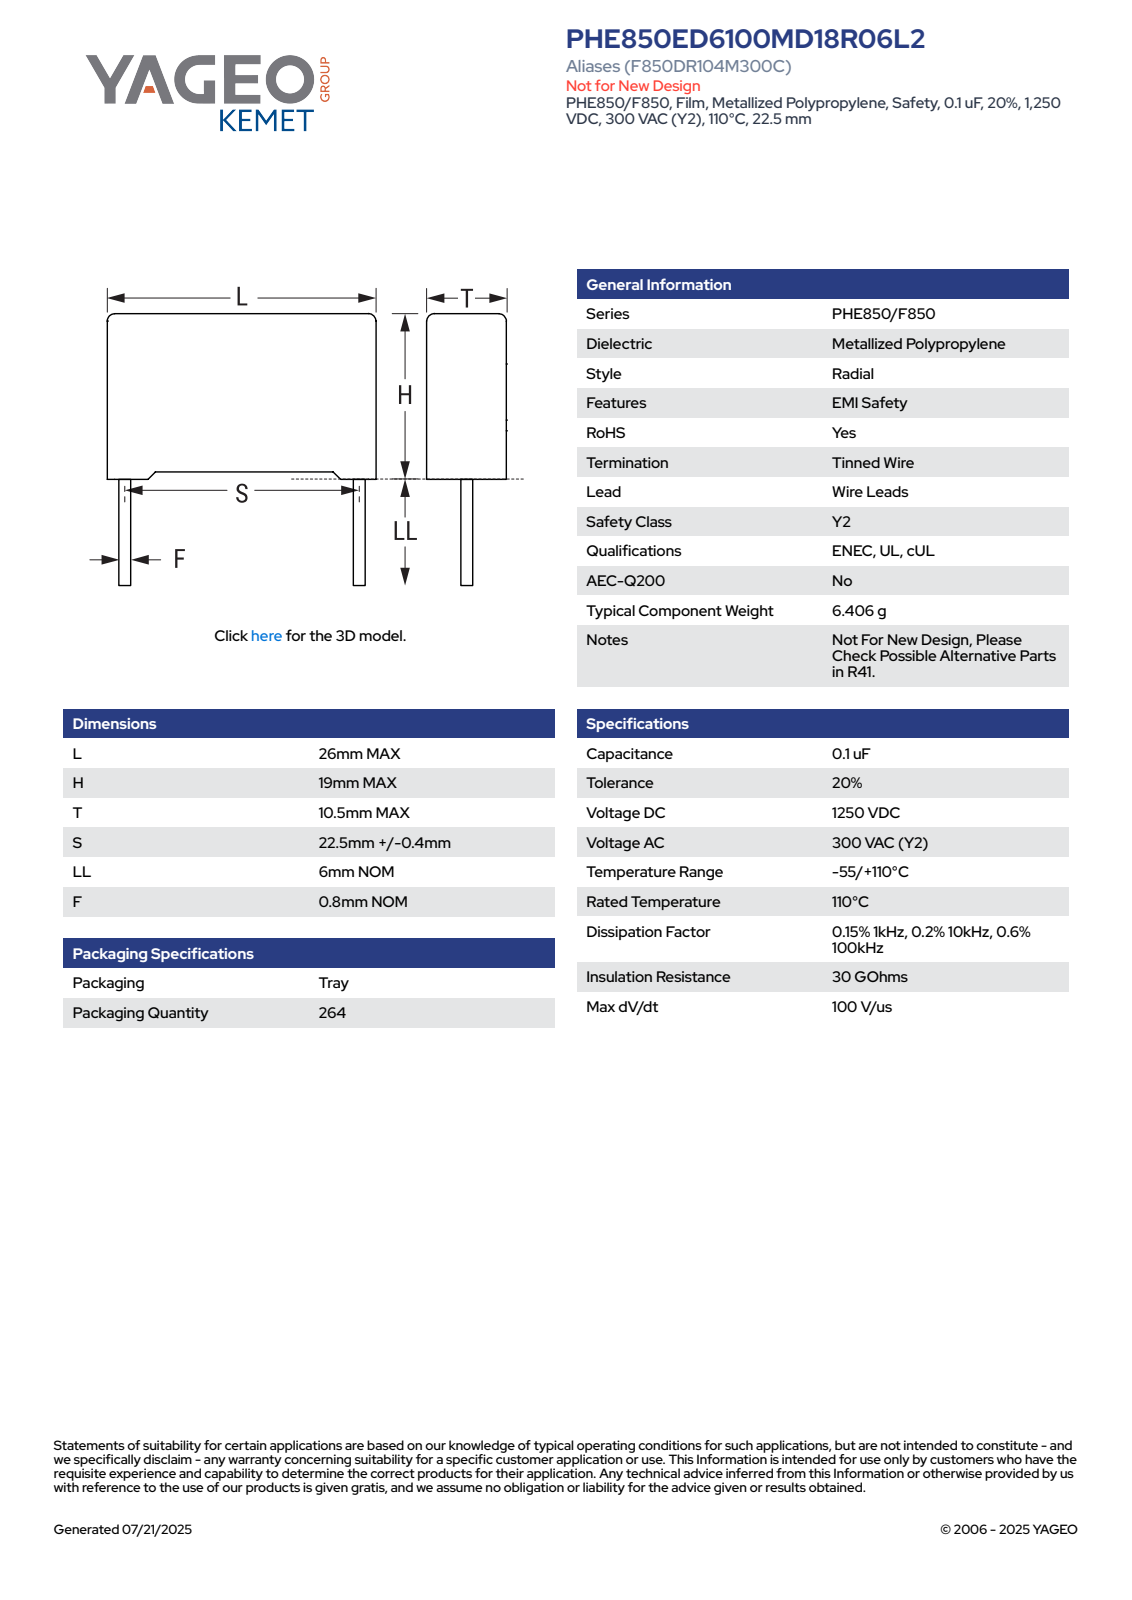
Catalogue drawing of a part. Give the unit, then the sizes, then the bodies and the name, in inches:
Units: inches
Overall size (bounding box): 1.024 × 0.984 × 0.414
Round bosses / shafts (diameter × count): ⌀0.031 ×2
Partial cylindrical surfaces — rounded edges, fillets, slot ends (radius × count): R0.02 ×4
Main face-to-face distances: 0.413, 0.719, 1.024, 0.722, 0.026, 0.03, 0.748, 0.034, 0.989, 0.414
Volume: 0.306 in³ · Surface area: 3.105 in²
Bodies: 4 solids, 85 faces (77 planar, 8 cylindrical, 0 other)
Part name (STEP PRODUCT): CFR_RB2_26X19X10.5_L26H19T10.5S22.5LL6F0.8
STEP written by: SolidWorks 2021 (AUTOMOTIVE_DESIGN)
